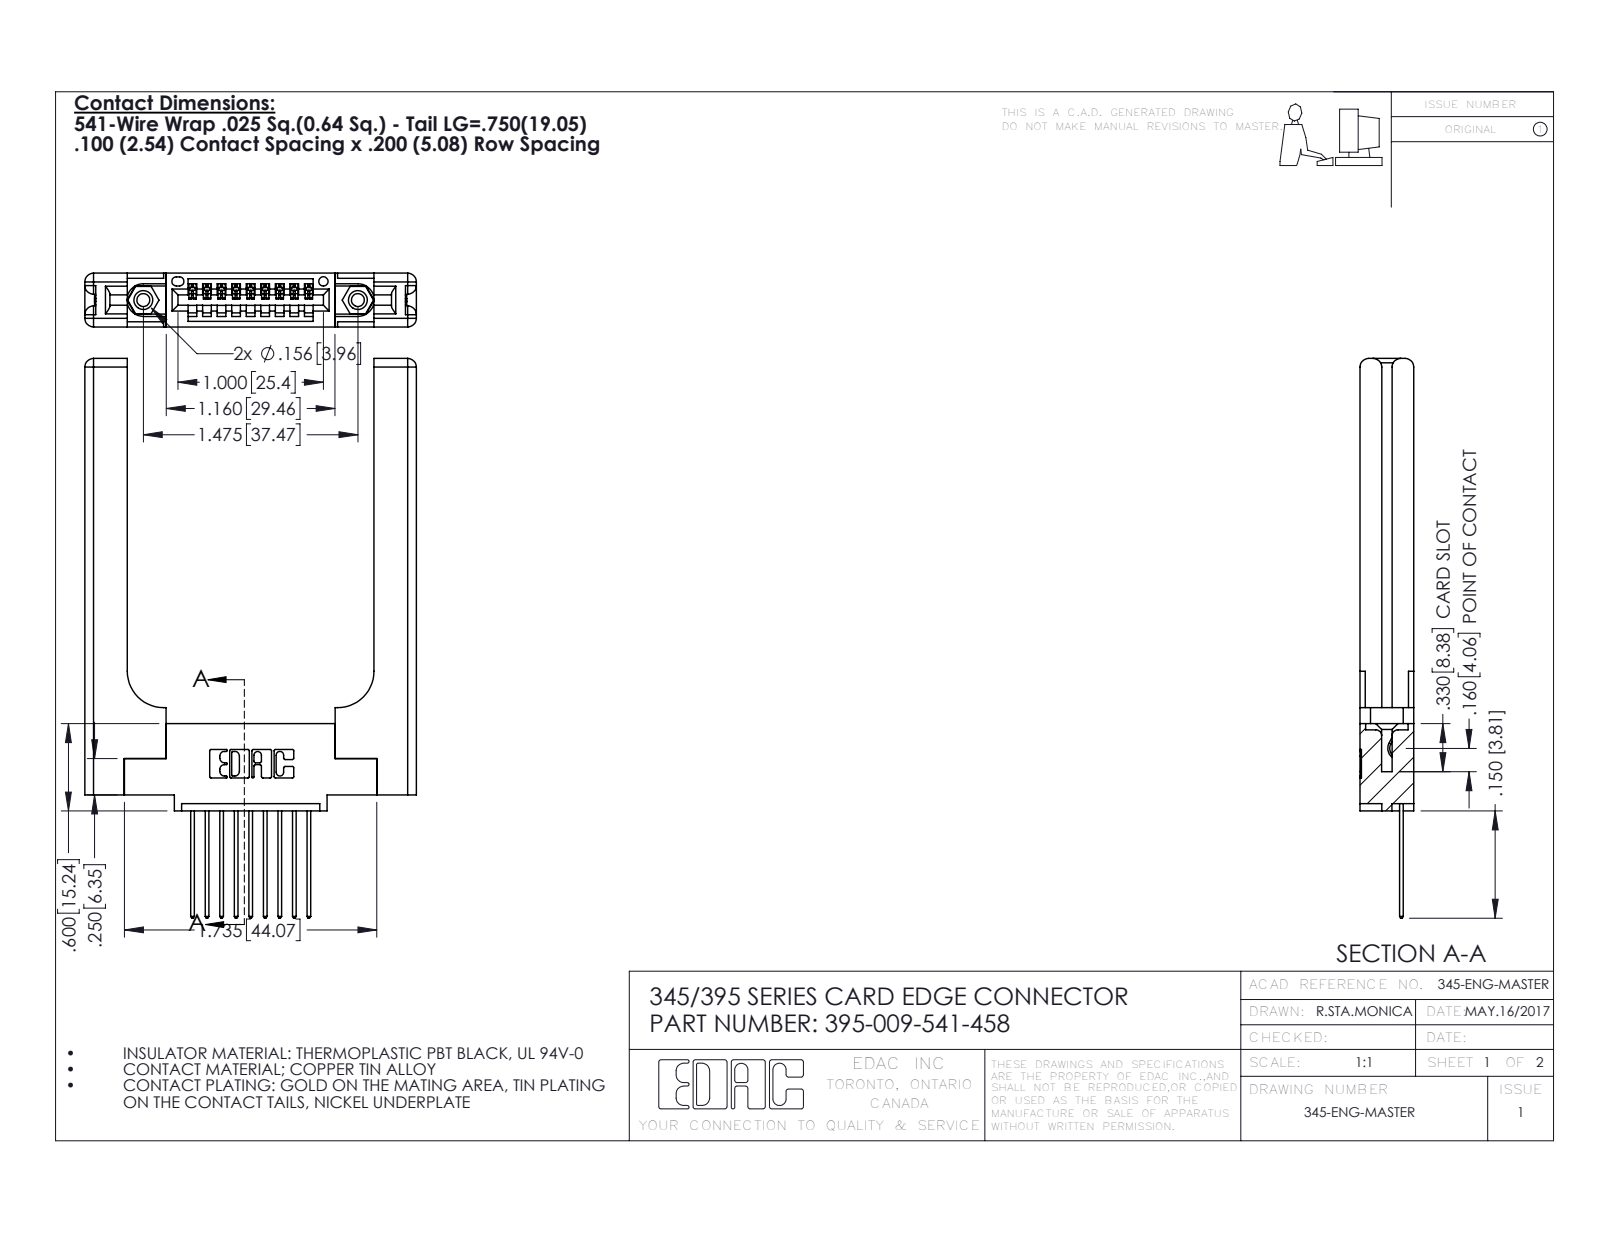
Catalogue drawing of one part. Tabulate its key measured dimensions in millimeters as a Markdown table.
| quantity | value |
| --- | --- |
| part name | 345 Part_0.110 Offset - 0.156 Dia-TH; 345-250-001_345-250-001-102; 345-292-001_345-293-141; 395-009-541-458 (+1 more) |
| STEP written by | SolidWorks 2016 (CONFIG_CONTROL_DESIGN) |
| units | millimeters |
| bodies | 14 solids, 908 faces (592 planar, 256 cylindrical, 60 other) |
| overall size | 97.7 × 57.9 × 9.4 |
| volume | 13 700 mm³ |
| surface area | 12 000 mm² |
| round holes (diameter × count) | 2.3 × 2, 3.2 × 2, 4 × 2, 1.6 × 1 |
| round bosses / shafts (diameter × count) | 3.9 × 2 |
| partial cylindrical surfaces (radius × count) | 0.3 × 22, 0.2 × 18, 0.3 × 18, 1.5 × 16, 0.2 × 6, 0.8 × 6, 0.7 × 3, 0.8 × 2 |
| main face-to-face distances | 9.4, 1.8, 3.8, 5.6, 2, 3.8, 7.6, 43.1, 1.8, 2.5 |
| hole center spacings | 6.9, 31.6, 37.5 |
